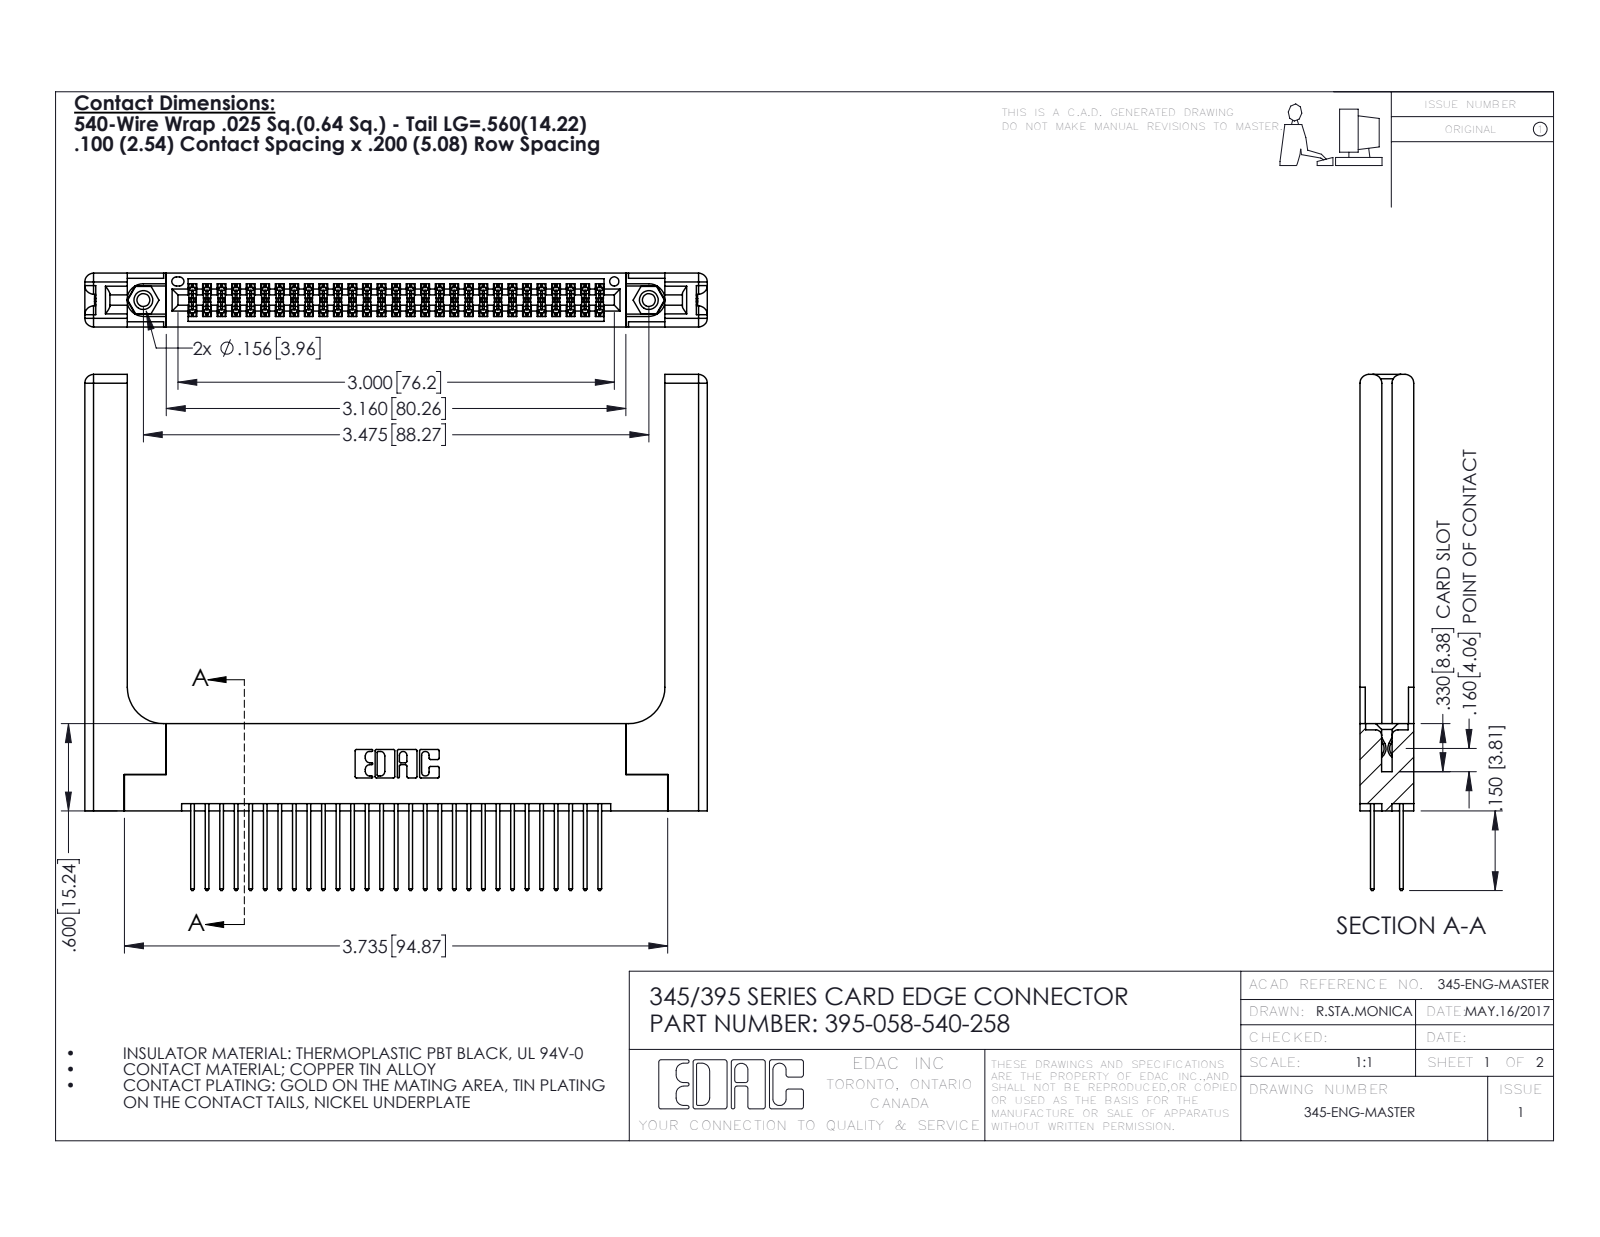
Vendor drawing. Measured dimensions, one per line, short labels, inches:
name: 345-292-001_345-293-140; 345-220-058_345-220-058; 395-058-540-258; 345-250-001_345-250-001-102 (+1 more)
written by: SolidWorks 2016 (CONFIG_CONTROL_DESIGN)
unit: in
bodies: 63 solids, 3282 faces (2142 planar, 1080 cylindrical, 60 other)
size: 4.279 × 3.547 × 0.37
volume: 1.168 in³; area: 33.45 in²
holes: 2× ⌀0.089, 2× ⌀0.125, 2× ⌀0.156, 1× ⌀0.064
bosses: 2× ⌀0.155
rounds: 87× R0.006, 58× R0.01, 22× R0.01, 16× R0.06, 6× R0.007, 6× R0.031, 3× R0.026, 2× R0.014
face distances: 0.072, 0.298, 0.37, 0.2, 0.098, 0.272, 0.025, 0.225, 0.148, 0.15
hole spacings: 0.27, 3.24, 3.475
